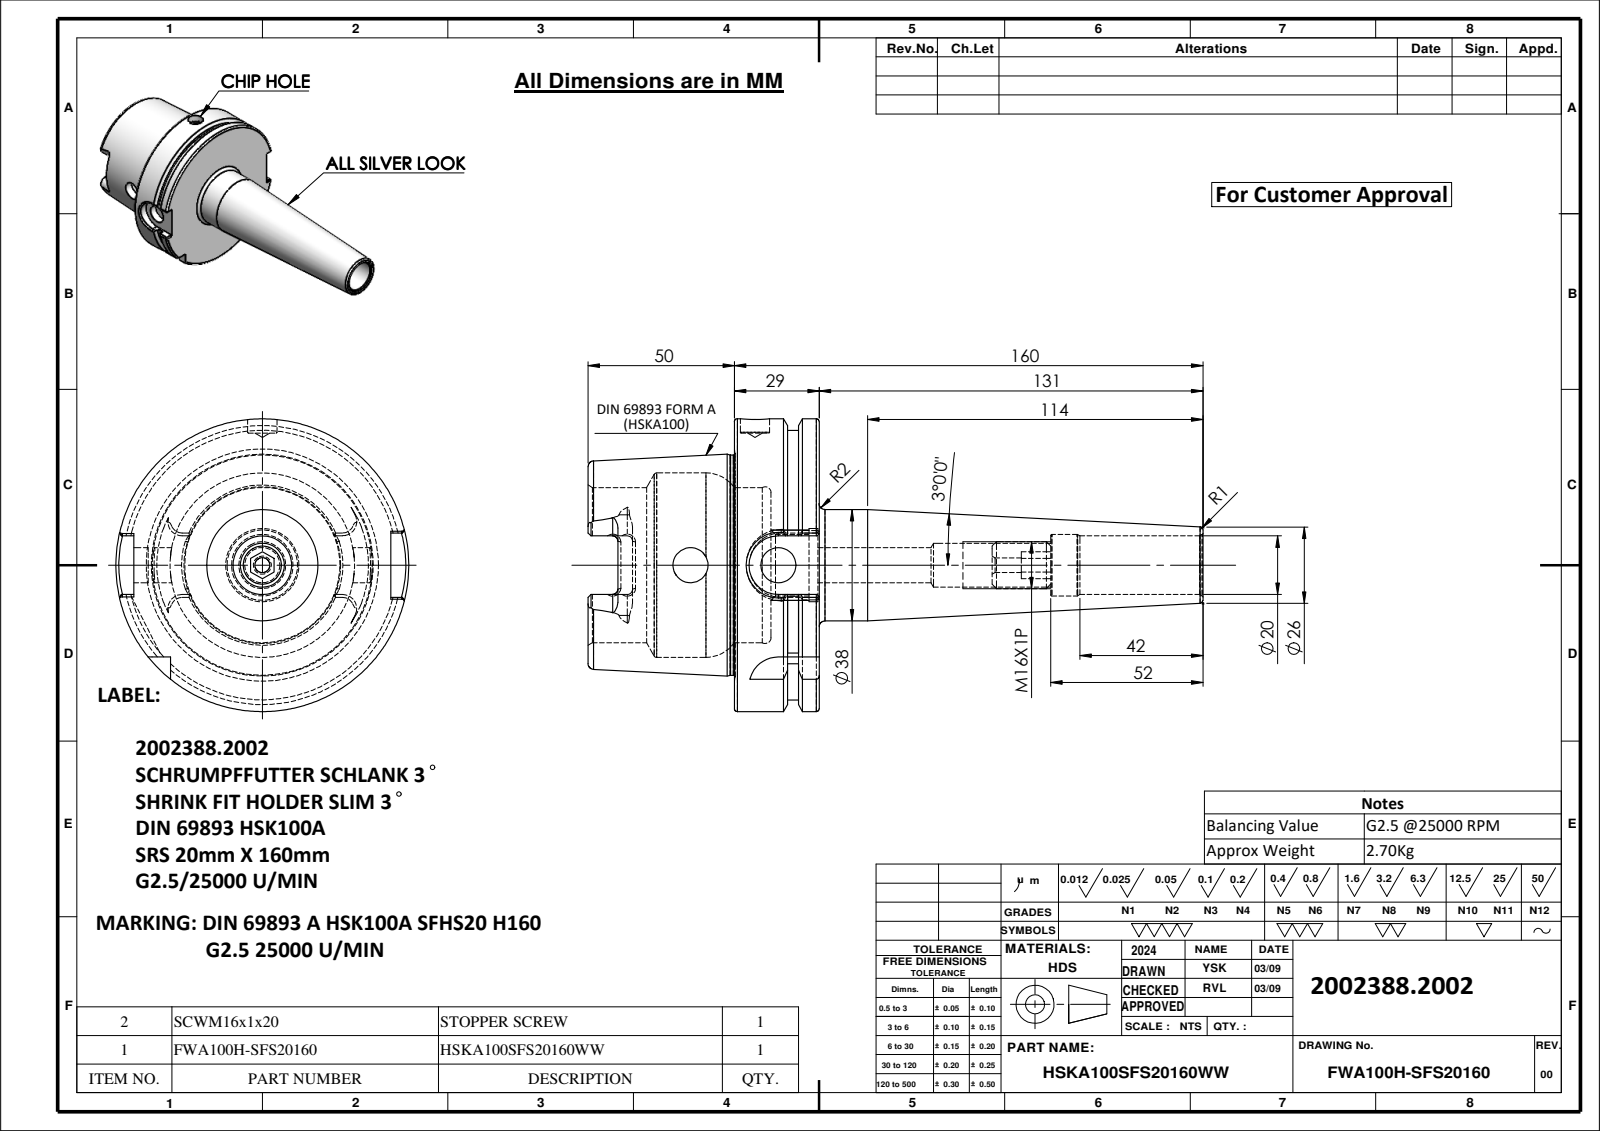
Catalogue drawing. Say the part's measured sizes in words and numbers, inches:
The part is named "FWA100H-SFS20160; HSKA100SFS20160WW; SCWM16X1P". Its 3-D file was written by "SolidWorks 2024 (CONFIG_CONTROL_DESIGN)". It is 2 solids with 205 faces: 61 planar, 58 cylindrical and 86 other. Overall it measures 8.268 by 3.937 by 3.937 inches. Its volume is 20.79 cubic inches and its surface area 109.7 square inches. Round holes: 3 of diameter 0.472, 1 of diameter 0.197, 1 of diameter 0.394, 1 of diameter 0.591, 1 of diameter 0.787, 1 of diameter 0.827, 1 of diameter 0.984, 1 of diameter 2.087, 1 of diameter 2.48. Round bosses or shafts: 1 of diameter 3.937, 1 of diameter 3.622, 1 of diameter 2.959, 1 of diameter 1.496, 1 of diameter 0.63. Partial cylindrical surfaces (rounded edges, fillets, slot ends): 6 of radius 0.071, 4 of radius 0.192, 2 of radius 0.394, 1 of radius 0.433. The main face-to-face distances are 1.14, 0.492, 0.648, 2.461, 1.969, 3.108, 2.83, 0.861, 0.369, 0.279. The hole center spacings are 1.181.
